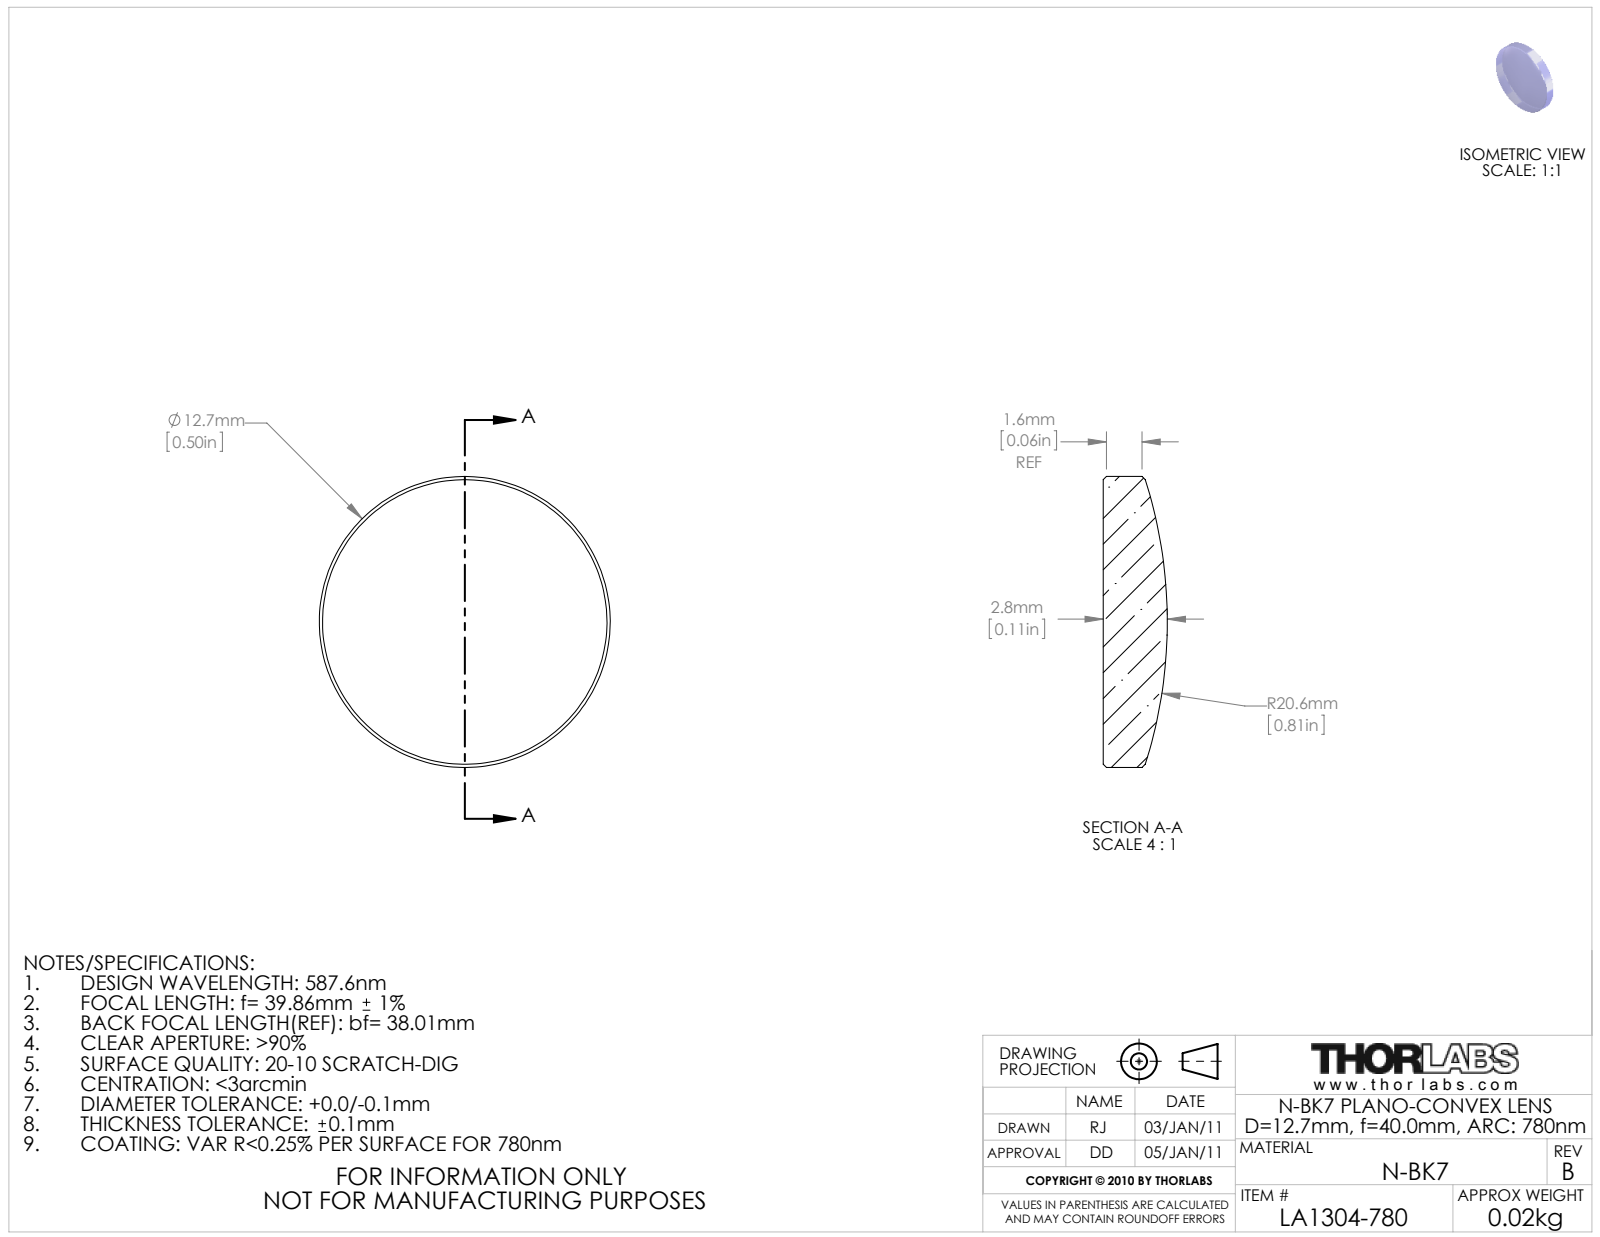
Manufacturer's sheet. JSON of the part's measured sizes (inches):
{"part_name": "21781-E0W", "step_written_by": "SolidWorks 2011 (AUTOMOTIVE_DESIGN)", "units": "inches", "bodies": {"solids": 0, "faces": 9, "planar": 1, "cylindrical": 2, "other": 6}, "overall_size": [0.5, 0.5, 0.11], "round_bosses_or_shafts": [[0.5, 1]]}
